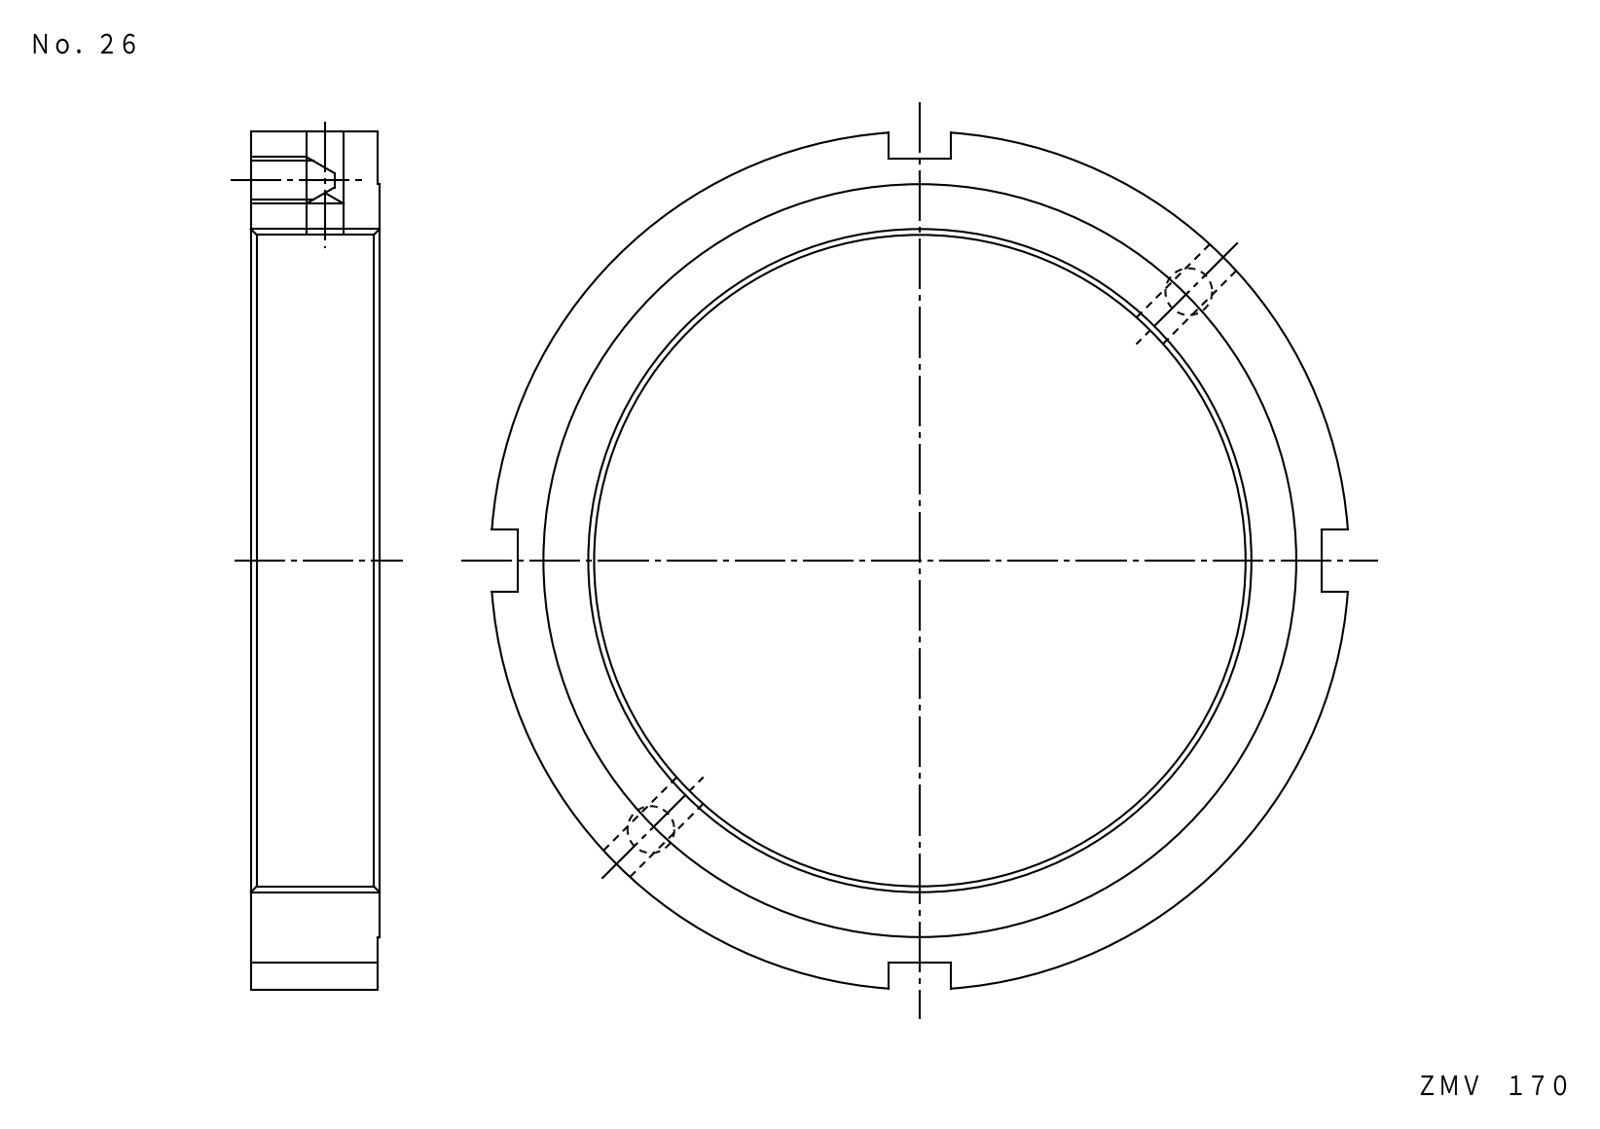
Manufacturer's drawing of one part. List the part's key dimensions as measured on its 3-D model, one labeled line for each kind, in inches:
Part name (STEP PRODUCT): FKD ZMV170
STEP written by: Autodesk Inventor LT (CONFIG_CONTROL_DESIGN)
Units: inches
Bodies: 1 solid, 29 faces (15 planar, 10 cylindrical, 4 other)
Overall size (bounding box): 8.639 × 8.639 × 1.299
Volume: 29.33 in³ · Surface area: 114.3 in²
Round holes (diameter × count): ⌀0.378 ×2, ⌀0.398 ×2, ⌀6.693 ×1
Round bosses / shafts (diameter × count): ⌀8.661 ×1, ⌀7.598 ×1
Main face-to-face distances: 1.28, 0.02, 1.299, 3.74, 4.37, 8.11, 0.63
Hole centre spacings: 3.839, 7.677
